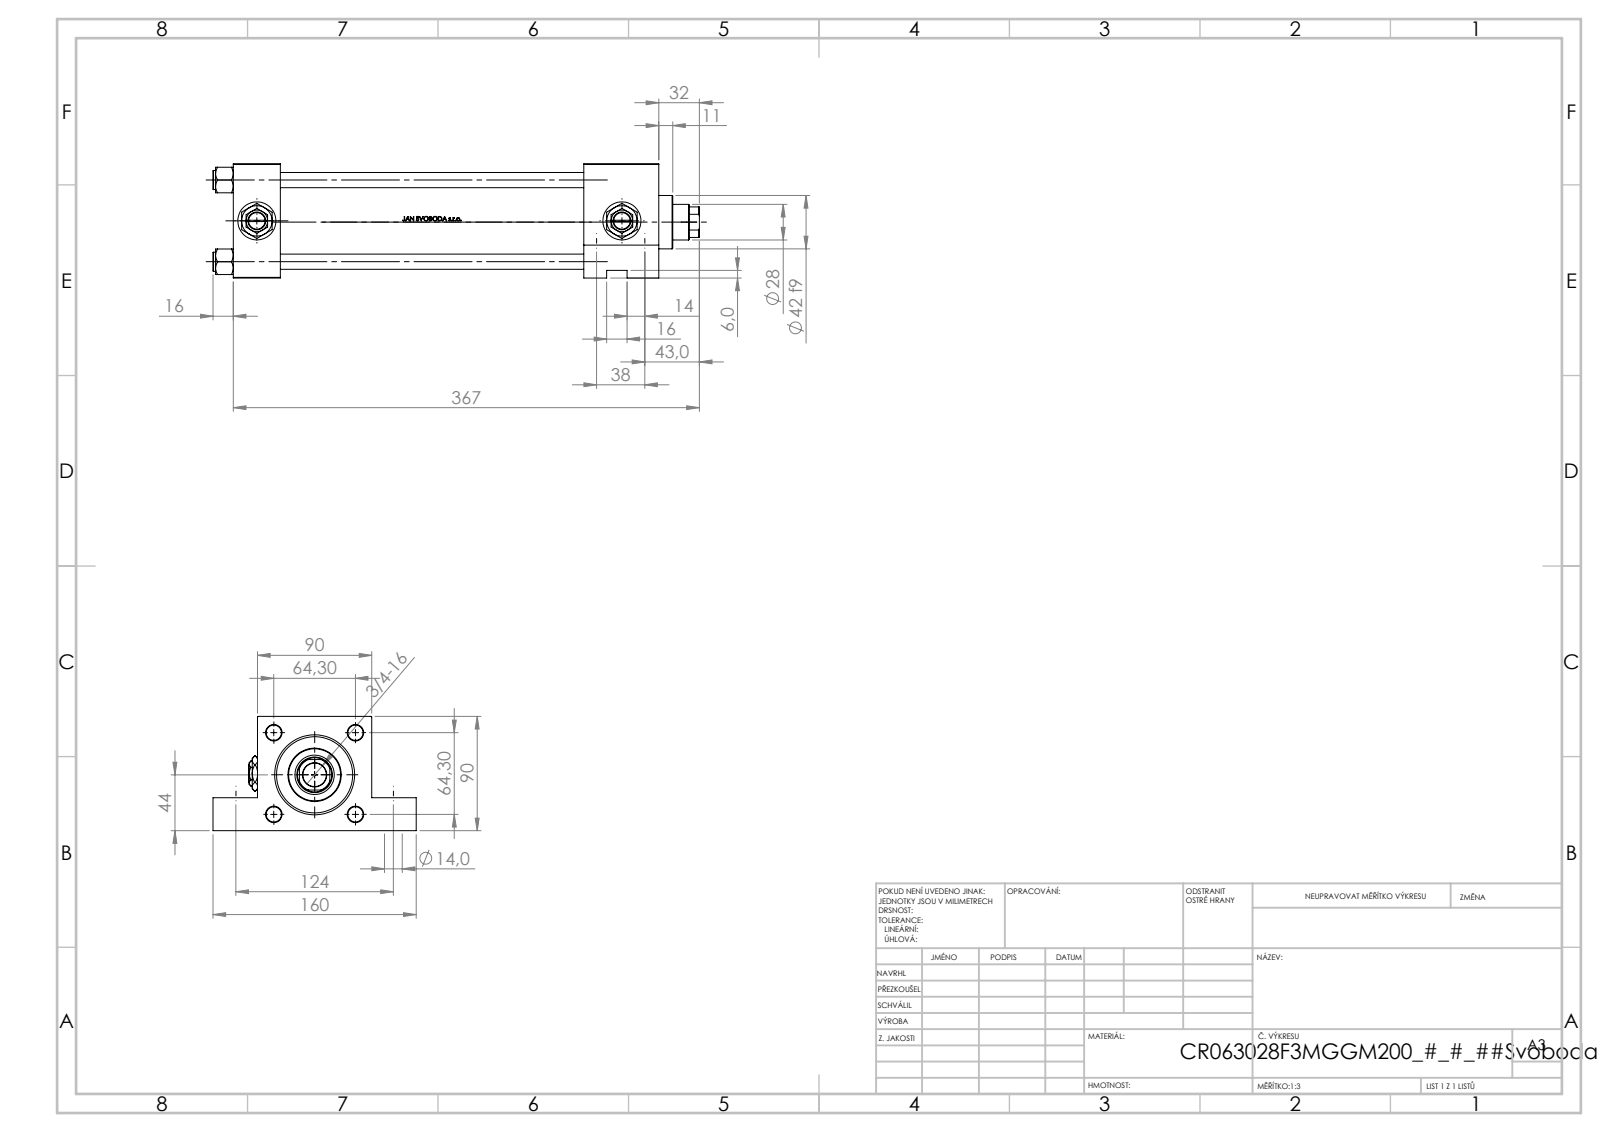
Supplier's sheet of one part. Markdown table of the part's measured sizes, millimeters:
| quantity | value |
| --- | --- |
| part name | V215CR_VCP_F; V215_VC_A; V215CR_F_Body; NUT_M5_F (+2 more) |
| STEP written by | SolidWorks 2019 (CONFIG_CONTROL_DESIGN) |
| units | millimeters |
| bodies | 13 solids, 1203 faces (485 planar, 136 cylindrical, 582 other) |
| overall size | 383 × 160 × 90 |
| volume | 1 327 000 mm³ |
| surface area | 316 376 mm² |
| round holes (diameter × count) | 12 × 4, 14 × 4, 20.96 × 4, 30 × 4, 7 × 3, 18.5 × 1, 28 × 1, 31 × 1, 50 × 1, 60 × 1, 63 × 1 |
| round bosses / shafts (diameter × count) | 15 × 4, 69 × 1, 42 × 1 |
| partial cylindrical surfaces (radius × count) | 13.5 × 1 |
| main face-to-face distances | 90, 37, 335, 298, 276, 239, 59, 26, 64, 306.3 |
| hole center spacings | 64.3, 38, 44.77, 46.18, 62.8, 68.03, 90.93, 124 |
